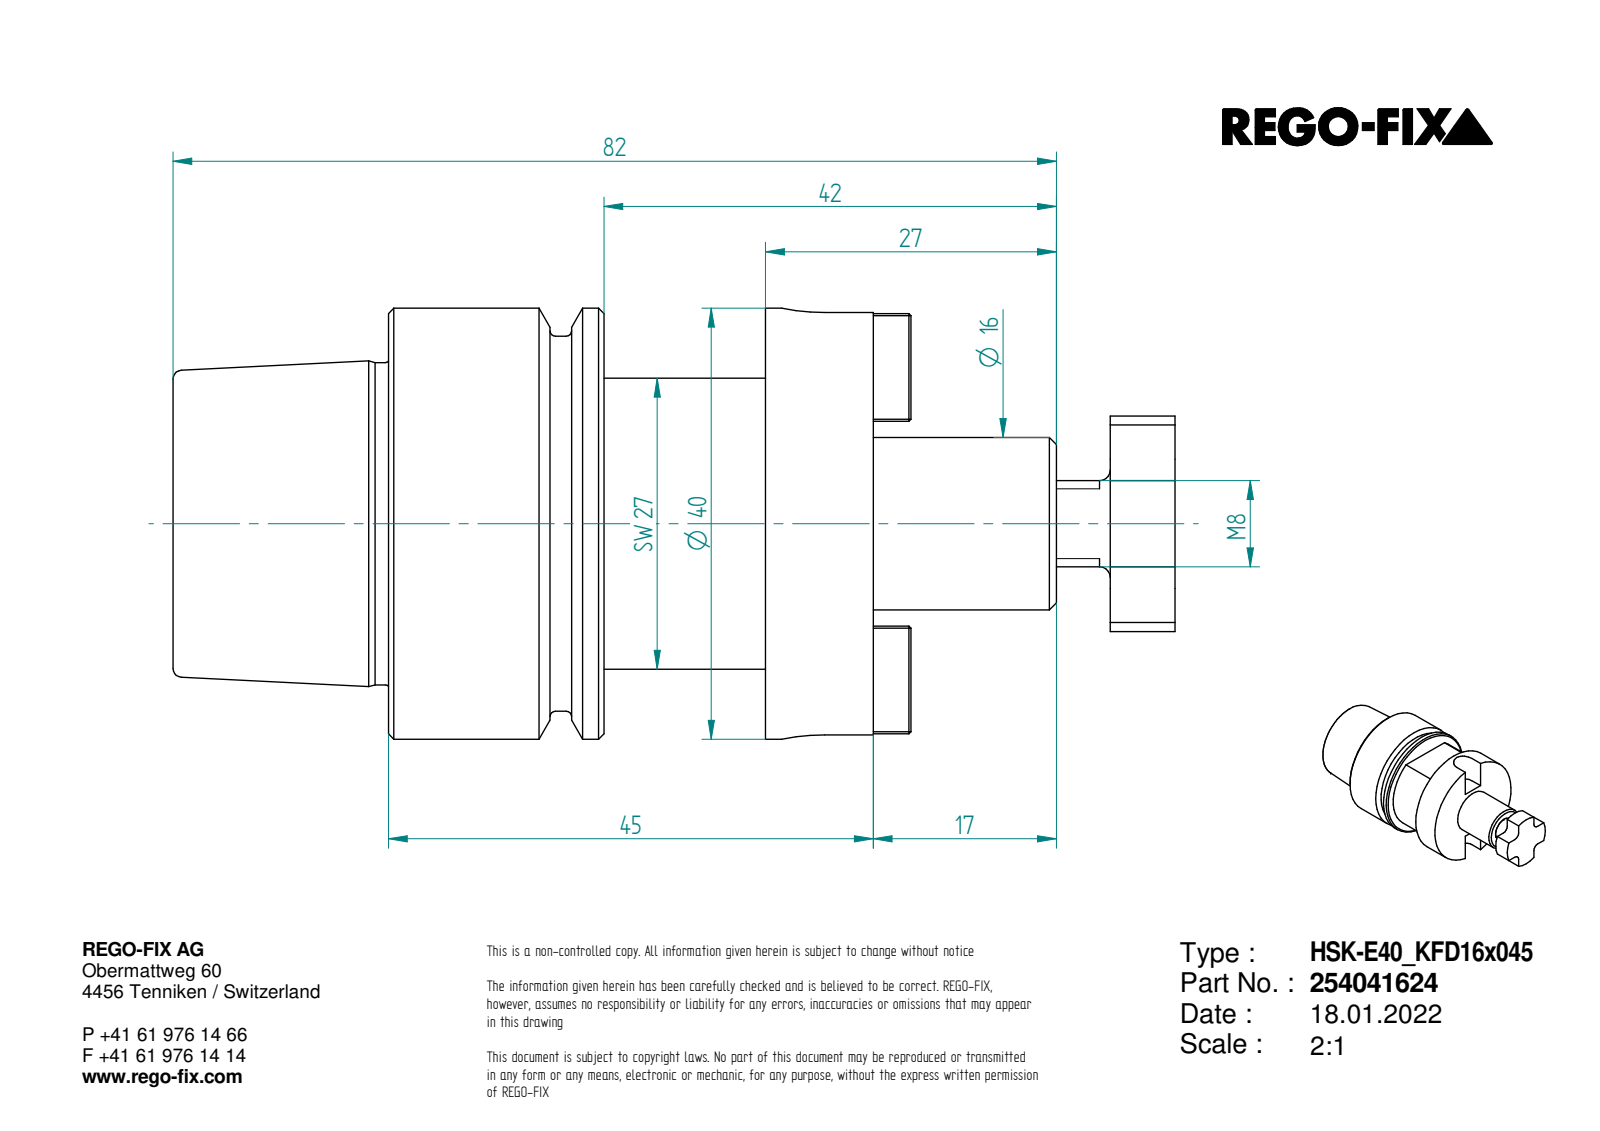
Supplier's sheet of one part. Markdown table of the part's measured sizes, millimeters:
| quantity | value |
| --- | --- |
| part name | 0025644 |
| STEP written by | ST-DEVELOPER v16.7 (AUTOMOTIVE_DESIGN) |
| units | millimeters |
| bodies | 4 solids, 119 faces (65 planar, 27 cylindrical, 27 other) |
| overall size | 93 × 40 × 40 |
| volume | 56 238 mm³ |
| surface area | 16 746 mm² |
| round holes (diameter × count) | 5 × 1, 10.92 × 1, 13 × 1, 21 × 1, 25.5 × 1 |
| round bosses / shafts (diameter × count) | 40 × 1, 34.8 × 1, 29.91 × 1, 16 × 1, 8 × 1 |
| partial cylindrical surfaces (radius × count) | 2 × 4, 4 × 1, 10 × 1, 16.85 × 1 |
| main face-to-face distances | 10, 8, 20, 27, 15, 35, 28, 45, 25, 4 |
